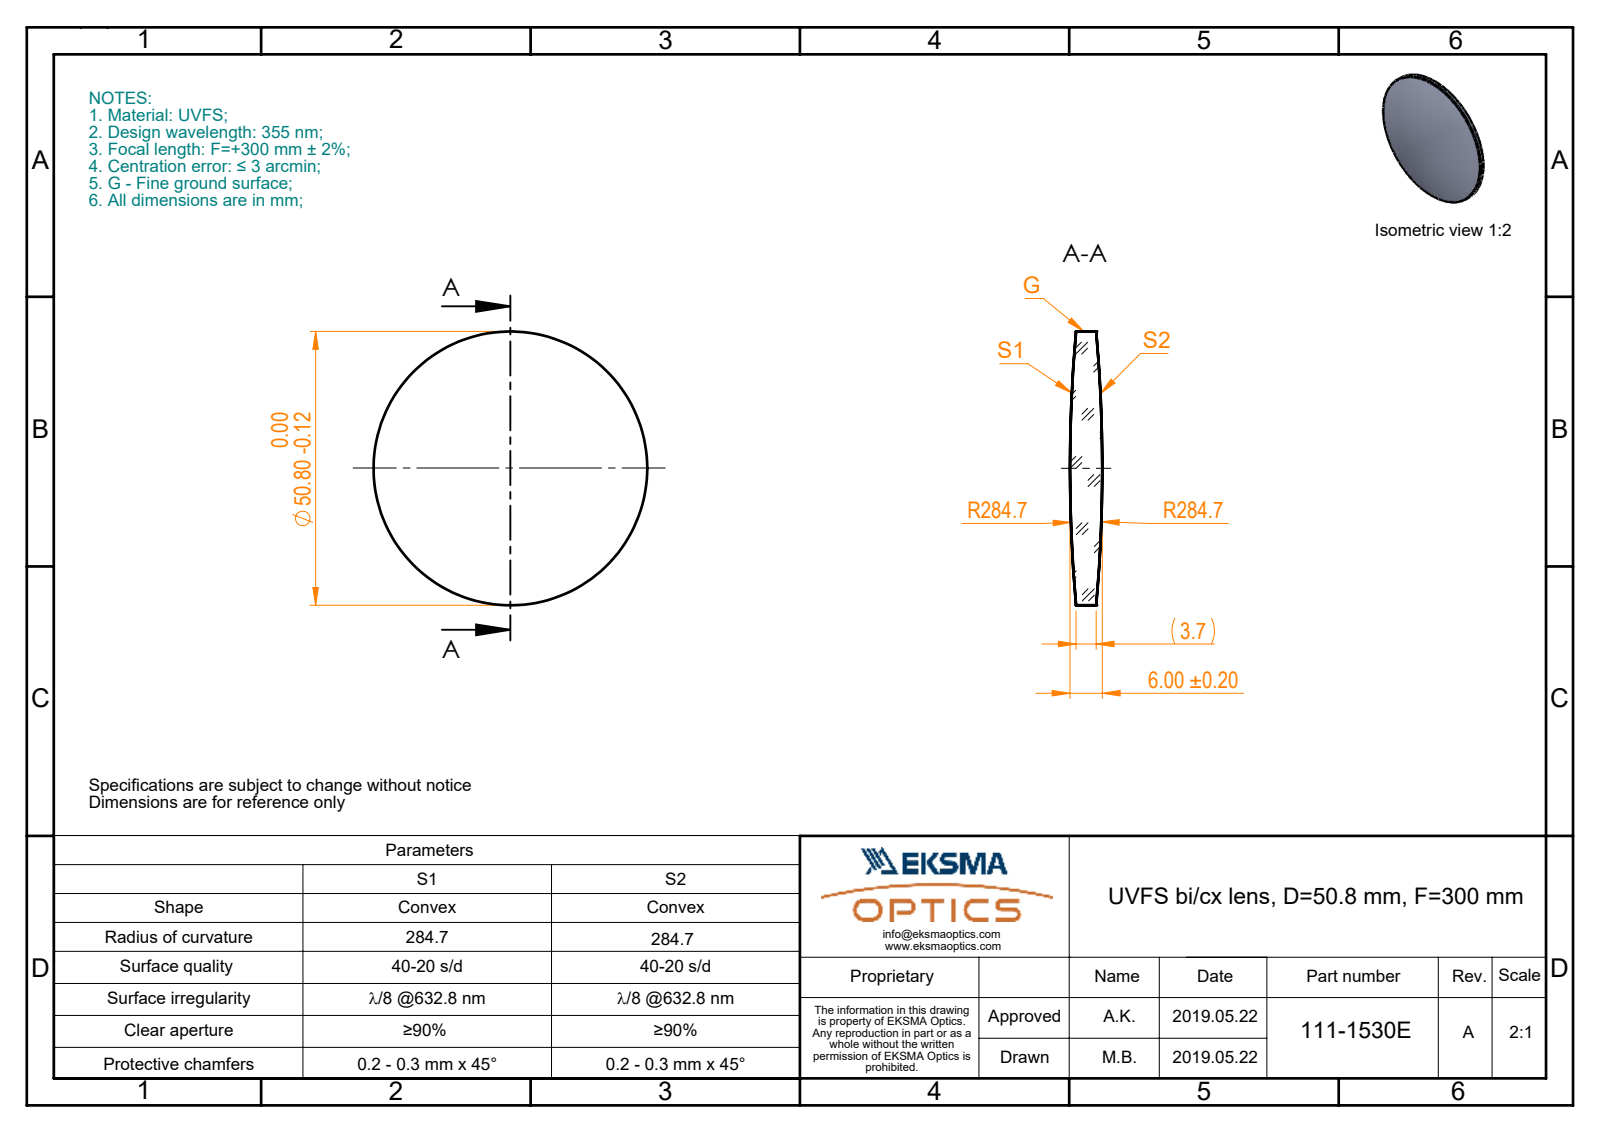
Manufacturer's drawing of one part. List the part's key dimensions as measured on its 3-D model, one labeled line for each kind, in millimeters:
Part name (STEP PRODUCT): 111-1530E UVFS bi-cx 50.8 F300
STEP written by: SolidWorks 2017 (CONFIG_CONTROL_DESIGN)
Units: millimetres
Bodies: 1 solid, 6 faces (0 planar, 2 cylindrical, 4 other)
Overall size (bounding box): 50.8 × 50.8 × 6
Volume: 9 861 mm³ · Surface area: 4 657 mm²
Round bosses / shafts (diameter × count): ⌀50.8 ×1
